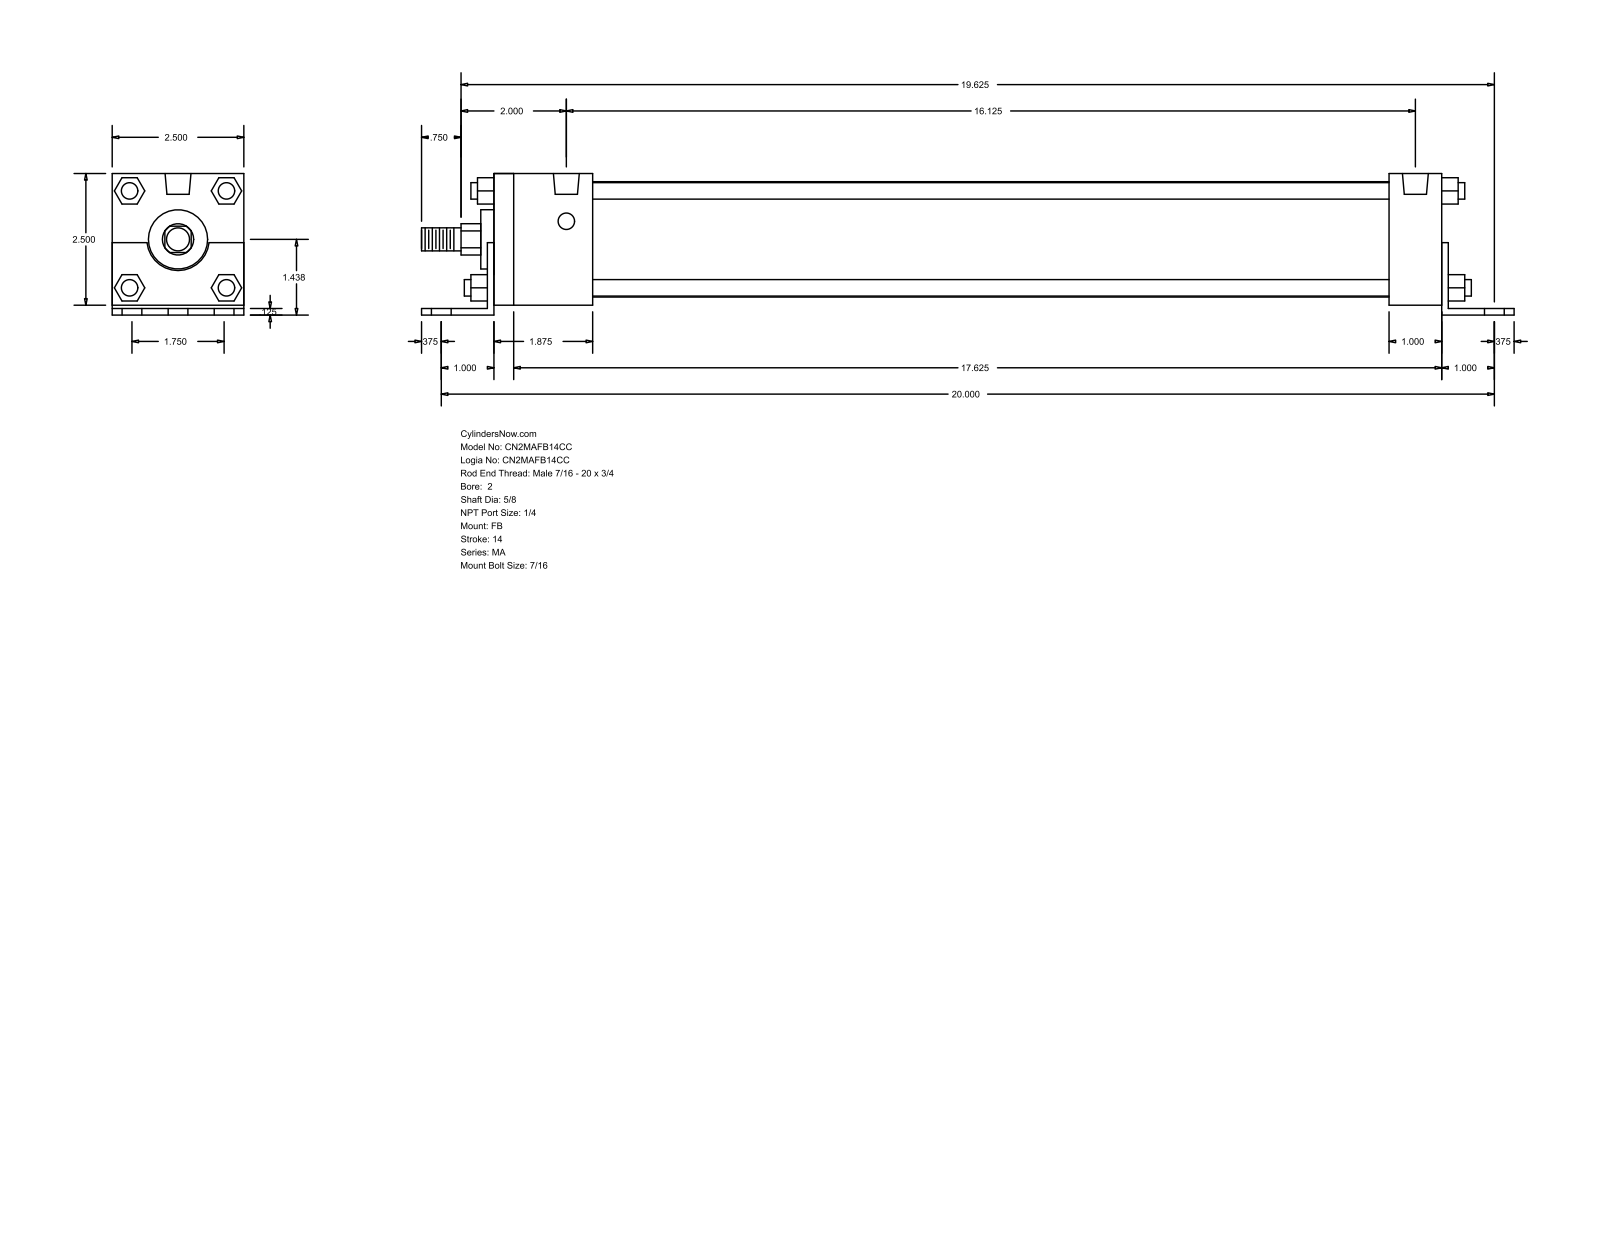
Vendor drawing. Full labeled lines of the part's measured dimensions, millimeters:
Part name (STEP PRODUCT): MA_FB__0200_0.625
STEP written by: GSSL Pune (CONFIG_CONTROL_DESIGN)
Units: millimetres
Bodies: 0 solids, 140 faces (105 planar, 35 cylindrical, 0 other)
Overall size (bounding box): 527.05 × 68.26 × 63.5
Round holes (diameter × count): ⌀11.11 ×6, ⌀7.94 ×4, ⌀12.49 ×2
Round bosses / shafts (diameter × count): ⌀7.94 ×4, ⌀55.63 ×1, ⌀28.57 ×1, ⌀15.88 ×1, ⌀11.11 ×1
Partial cylindrical surfaces — rounded edges, fillets, slot ends (radius × count): R7.54 ×1, R15.05 ×1
Main face-to-face distances: 63.5, 4.76, 3.17, 68.26, 1.59, 3.18, 65.09, 460.37, 457.19, 12.7
Hole centre spacings: 22.23, 508.5, 508.01, 44.11, 44.46, 64.3, 409.58, 448.23
